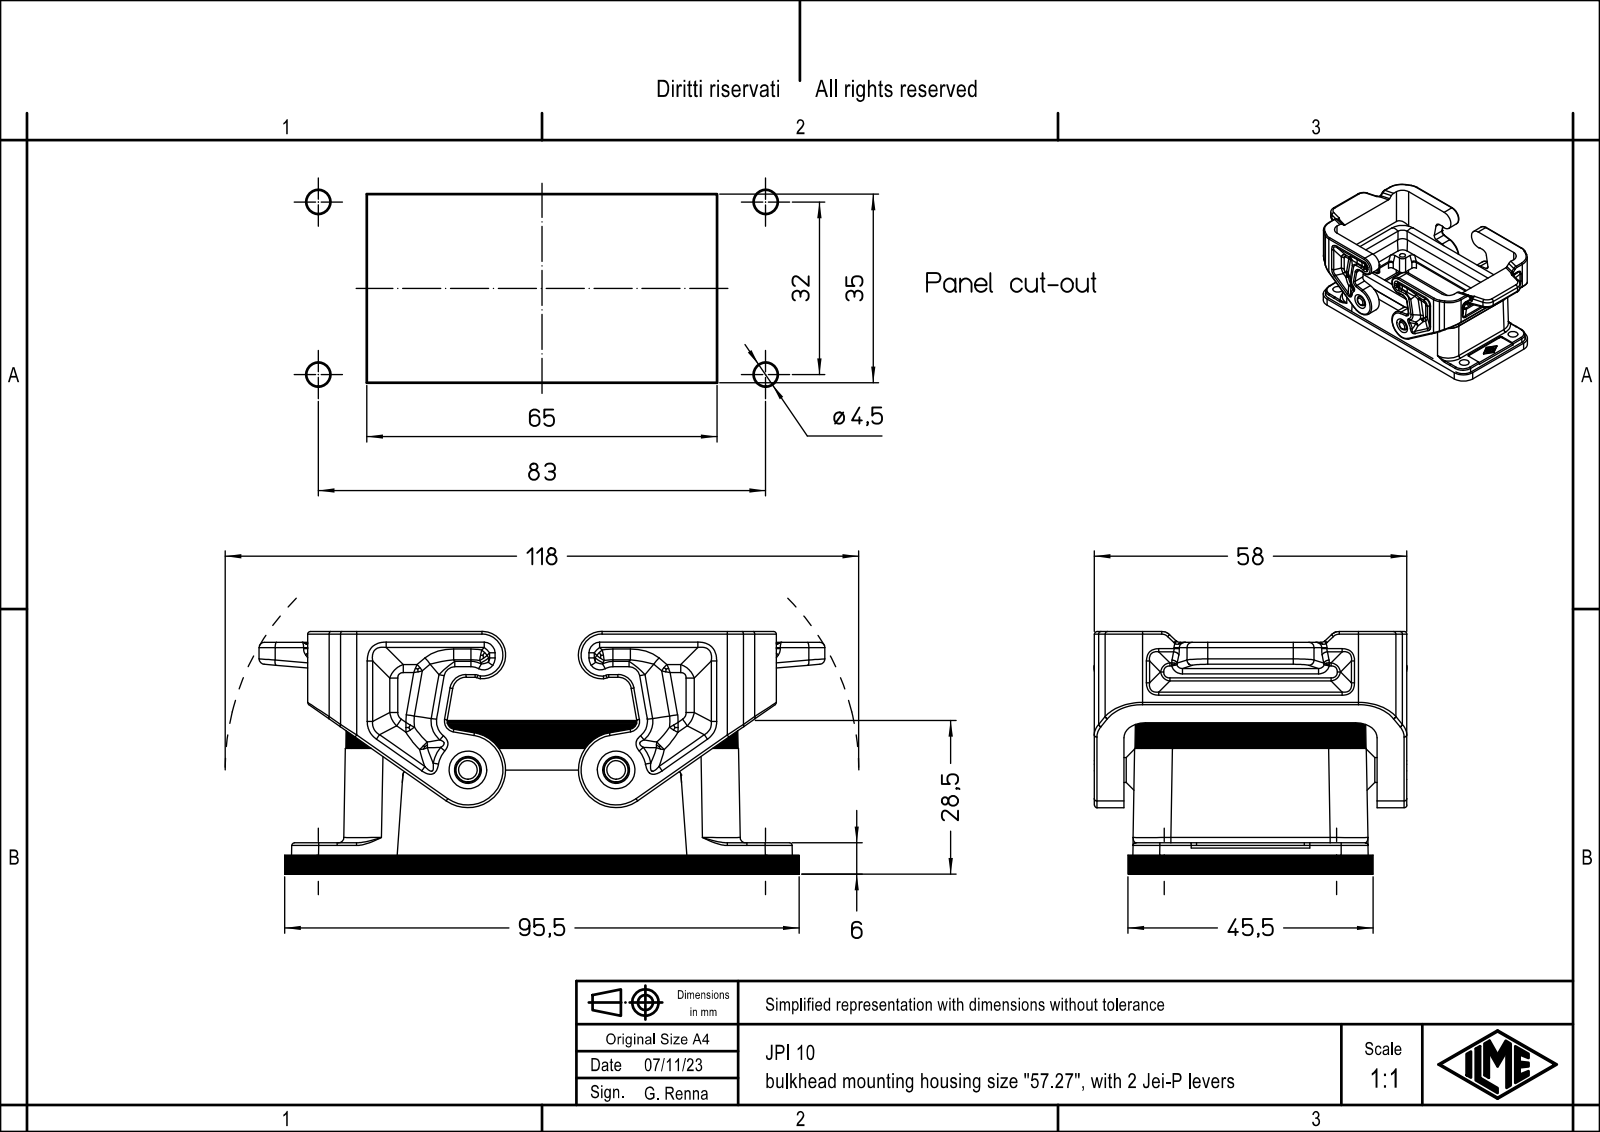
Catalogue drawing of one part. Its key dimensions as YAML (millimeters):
part_name: "JPI 10"
step_written_by: "Creo Elements/Direct Modeling 20.1B 02-Apr-2019 (C) Parametric Technology GmbH (AUTOMOTIVE_DESIGN)"
units: millimeters
bodies: {solids: 1, faces: 926, planar: 245, cylindrical: 299, other: 382}
overall_size: [105, 58.08, 45]
volume: 51232
surface_area: 31891
round_holes:
  - {diameter: 2.75, count: 4}
  - {diameter: 3.8, count: 4}
partial_cylinders:
  - {radius: 0.5, count: 50}
  - {radius: 1, count: 42}
  - {radius: 3, count: 34}
  - {radius: 2, count: 24}
  - {radius: 1.5, count: 20}
  - {radius: 4, count: 20}
  - {radius: 6, count: 16}
  - {radius: 0.17, count: 15}
face_to_face_distances: [47, 5.5, 52.5, 3.5, 45, 5.75, 3.03, 41.5, 39.5, 2]
hole_center_spacings: [13.24, 32.24, 70.04, 75.96, 27, 32, 57, 63.07]
